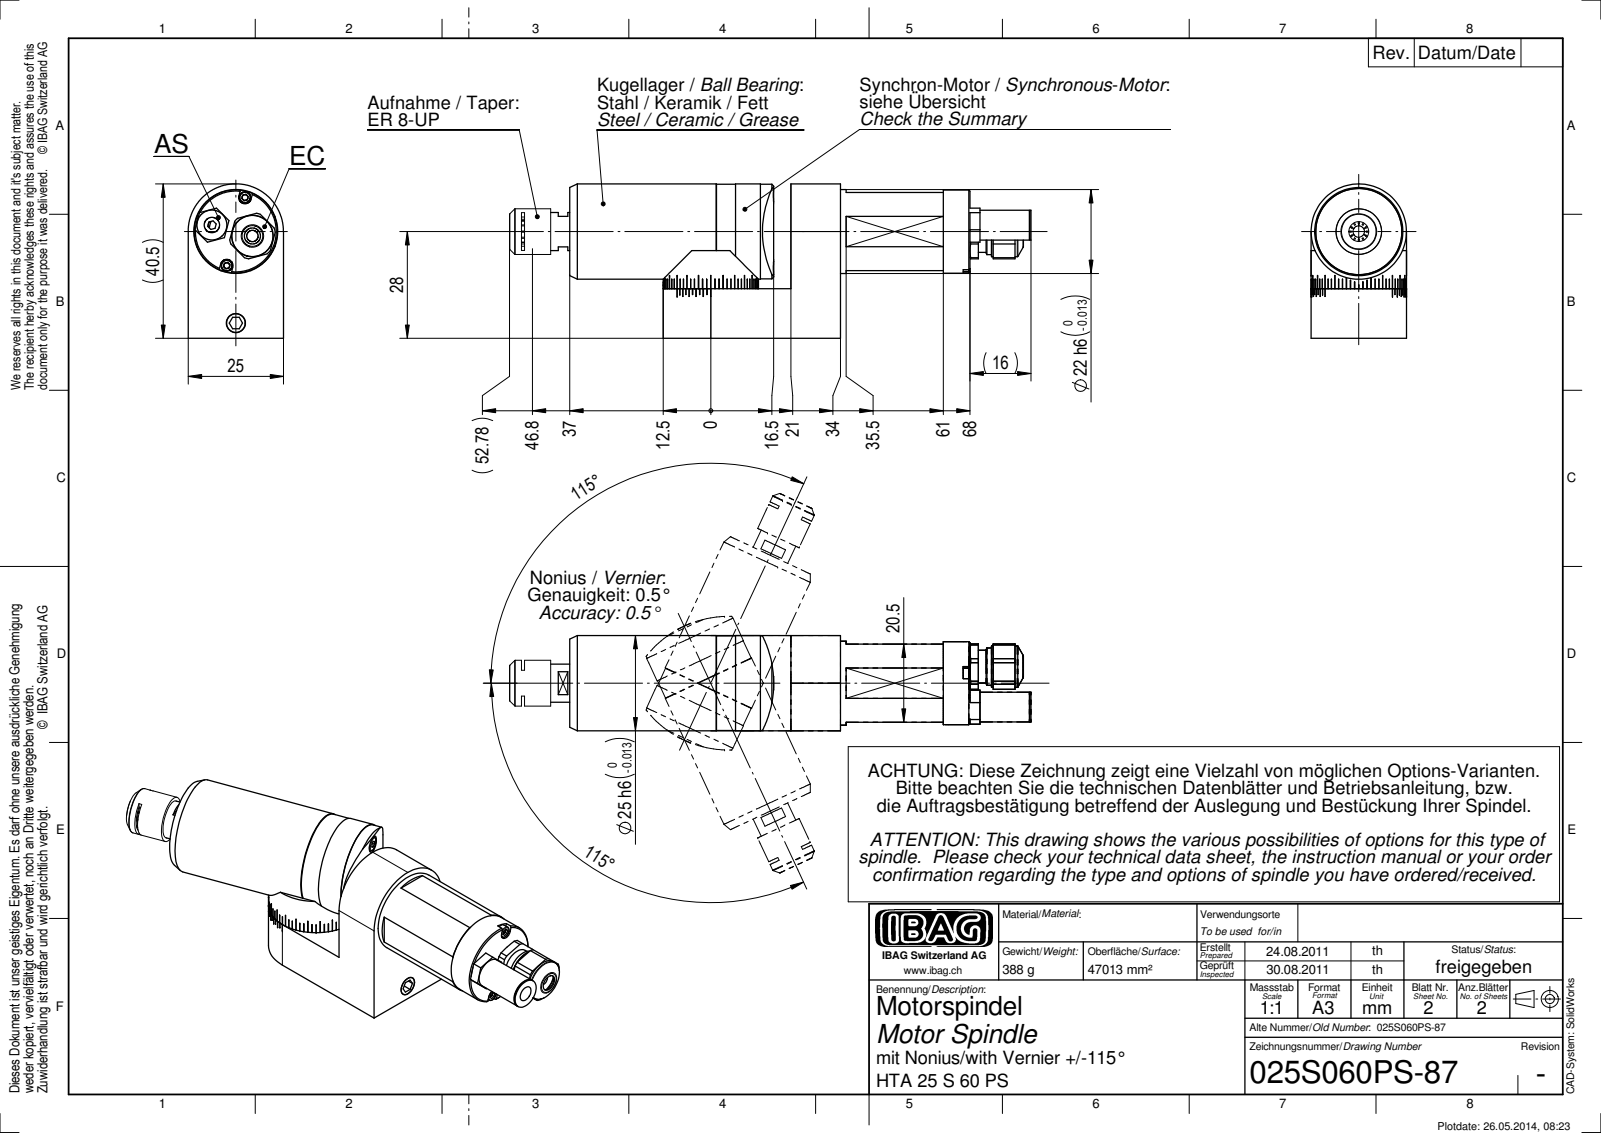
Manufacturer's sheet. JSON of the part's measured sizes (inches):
{"part_name": "025S060PS-87", "step_written_by": "SolidWorks 2010 (CONFIG_CONTROL_DESIGN)", "units": "inches", "bodies": {"solids": 0, "faces": 280, "planar": 133, "cylindrical": 103, "other": 44}, "overall_size": [5.385, 1.594, 0.984], "round_holes": [[0.118, 2], [0.157, 1], [0.165, 1], [0.173, 1], [0.197, 1], [0.205, 1], [0.36, 1], [0.417, 1], [0.89, 1]], "round_bosses_or_shafts": [[0.984, 2], [0.118, 2], [0.976, 1], [0.866, 1], [0.858, 1], [0.472, 1], [0.429, 1], [0.394, 1]], "partial_cylinders_radius": [[0.061, 4], [0.114, 4], [0.065, 2], [0.167, 1], [0.201, 1], [0.238, 1], [0.254, 1], [0.376, 1]], "face_to_face_distances": [0.512, 0.984, 0.807, 0.089, 0.896, 2.795, 0.276, 0.315, 2.283, 4.134], "hole_center_spacings": [0.177, 0.256, 0.374, 0.395, 0.433, 0.453, 0.915, 0.945]}
